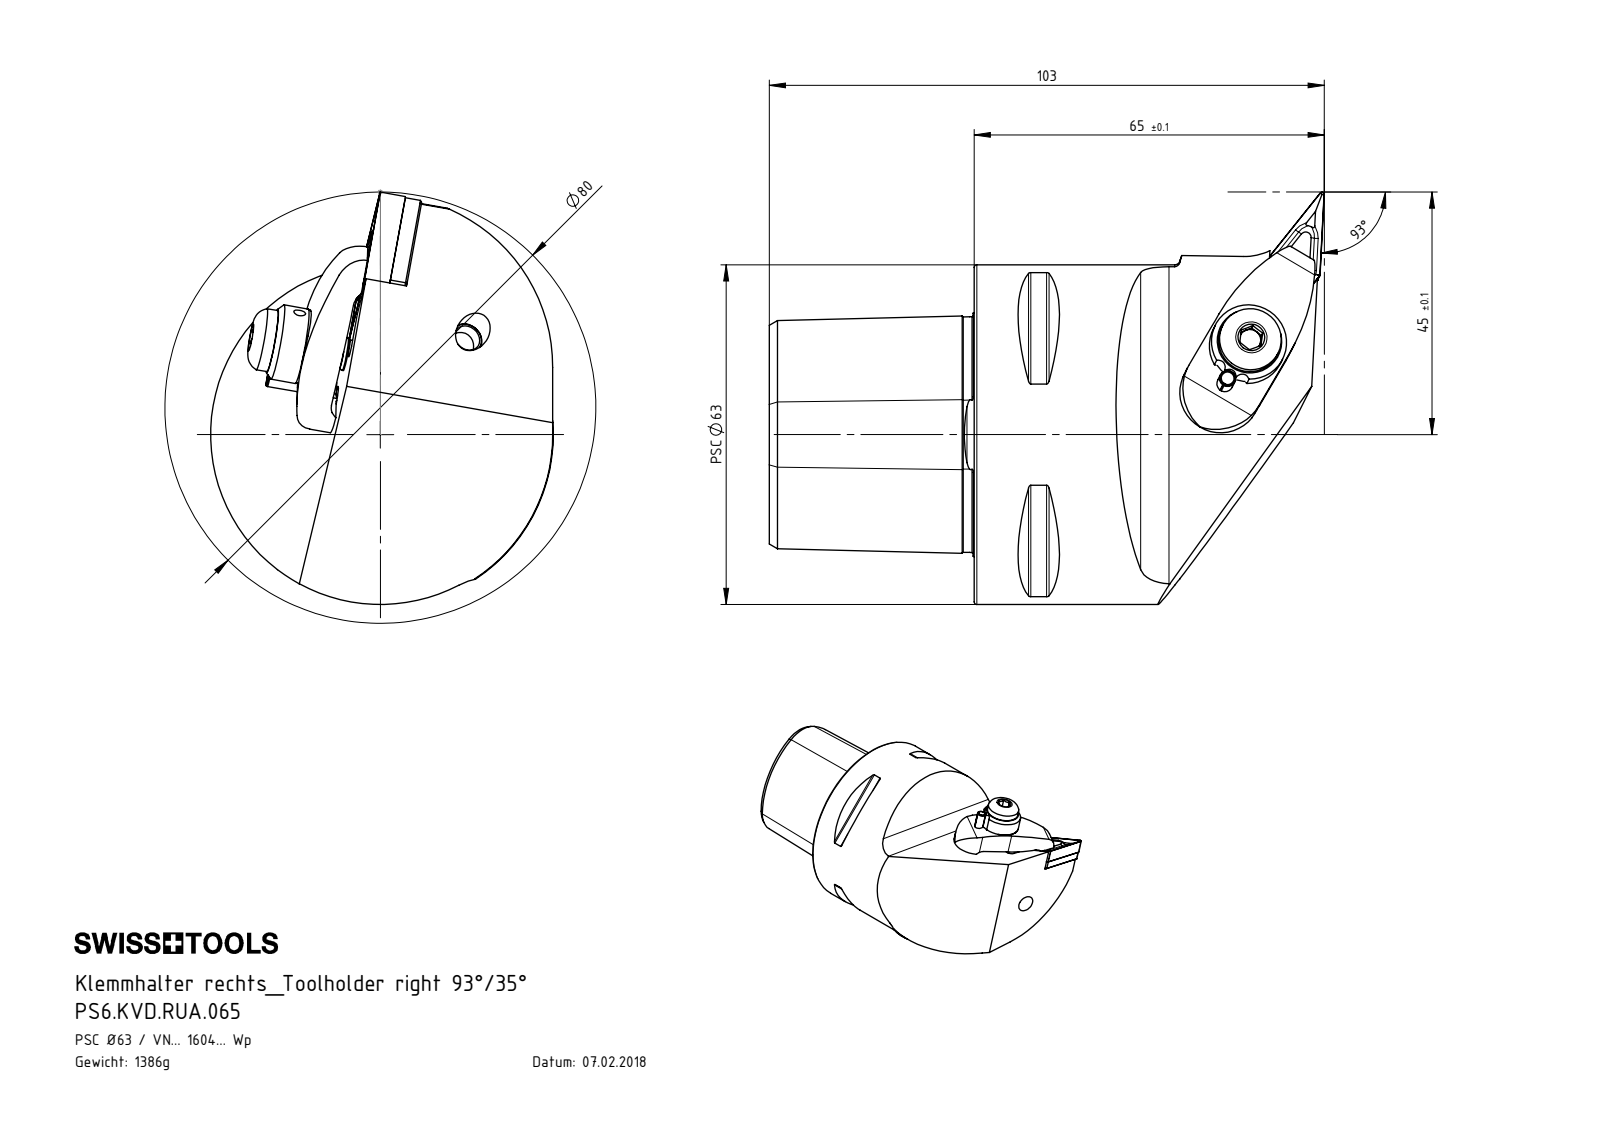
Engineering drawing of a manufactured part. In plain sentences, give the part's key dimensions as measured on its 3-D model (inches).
The part is named "VNMG160404; PS6.KVD.RUA.065; WCC-ER5.102.012_B; WCB-ER2.001.009_A (+6 more)". Its 3-D file was written by "SolidWorks 2017 (AUTOMOTIVE_DESIGN)". It is 10 solids with 429 faces: 100 planar, 132 cylindrical and 197 other. Overall it measures 4.055 by 3.012 by 2.504 inches. Its volume is 10.74 cubic inches and its surface area 52.02 square inches. Round holes: 3 of diameter 0.079, 3 of diameter 0.197, 2 of diameter 0.276, 1 of diameter 0.094, 1 of diameter 0.118, 1 of diameter 0.13, 1 of diameter 0.15, 1 of diameter 0.157, 1 of diameter 0.195, 1 of diameter 0.236, 1 of diameter 0.244, 1 of diameter 0.272. Round bosses or shafts: 2 of diameter 0.236, 2 of diameter 0.157, 2 of diameter 0.118, 1 of diameter 2.48, 1 of diameter 0.551, 1 of diameter 0.453, 1 of diameter 0.268, 1 of diameter 0.244. Partial cylindrical surfaces (rounded edges, fillets, slot ends): 10 of radius 0.02, 6 of radius 0.013, 6 of radius 0.023, 4 of radius 0.016, 3 of radius 0.059, 2 of radius 0.079, 2 of radius 0.118, 2 of radius 0.236. The main face-to-face distances are 1.496, 0.98, 0.051, 0.301, 0.125, 0.176, 0.352, 0.227, 1.063, 0.433. The hole center spacings are 0.316, 1.076, 0.323, 0.76, 0.76, 0.753, 0.753, 1.076.
